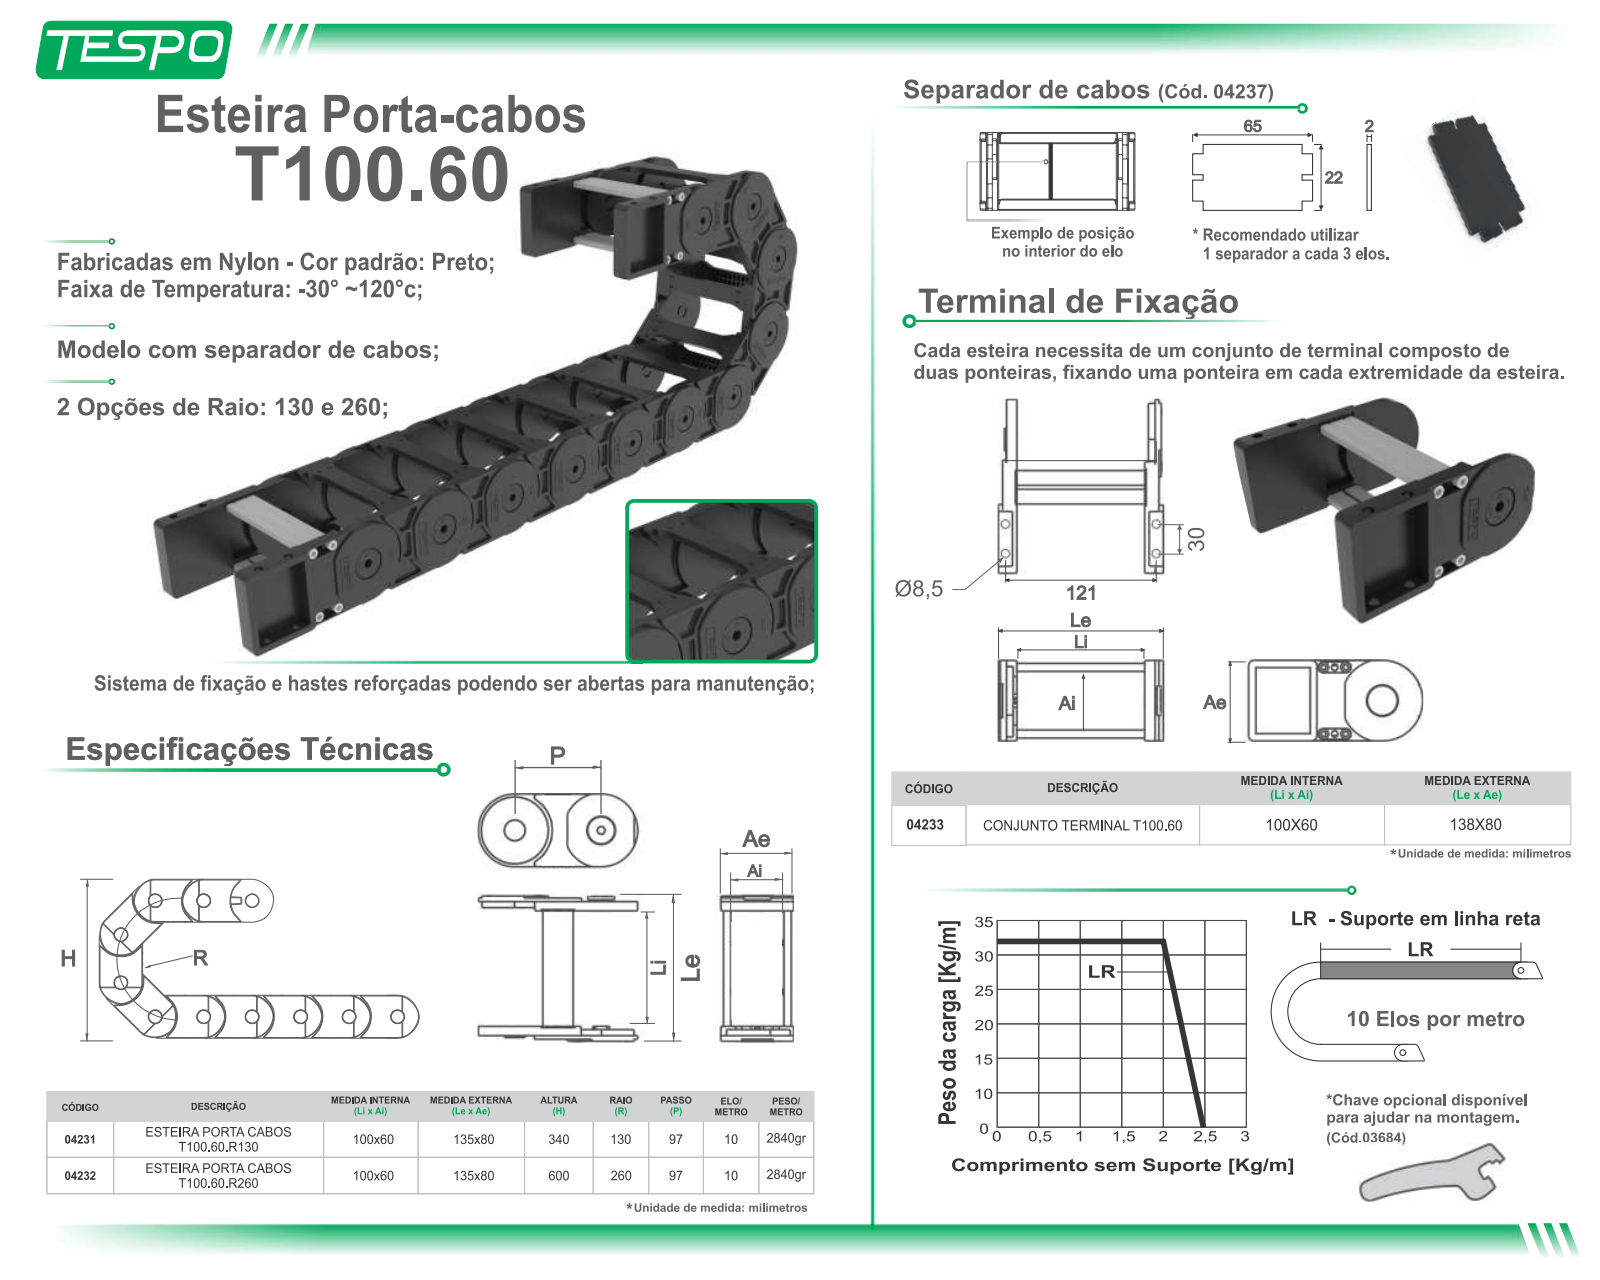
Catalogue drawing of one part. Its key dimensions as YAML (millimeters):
step_written_by: "ST-DEVELOPER v15 (AUTOMOTIVE_DESIGN)"
units: millimeters
bodies: {solids: 1, faces: 74, planar: 36, cylindrical: 0, other: 38}
overall_size: [179, 133.6, 82]
volume: 296128
surface_area: 88272
face_to_face_distances: [16.8, 116.8, 13.3, 120.3, 3.5, 103.5, 13.1, 120.5, 3.7, 103.7]
